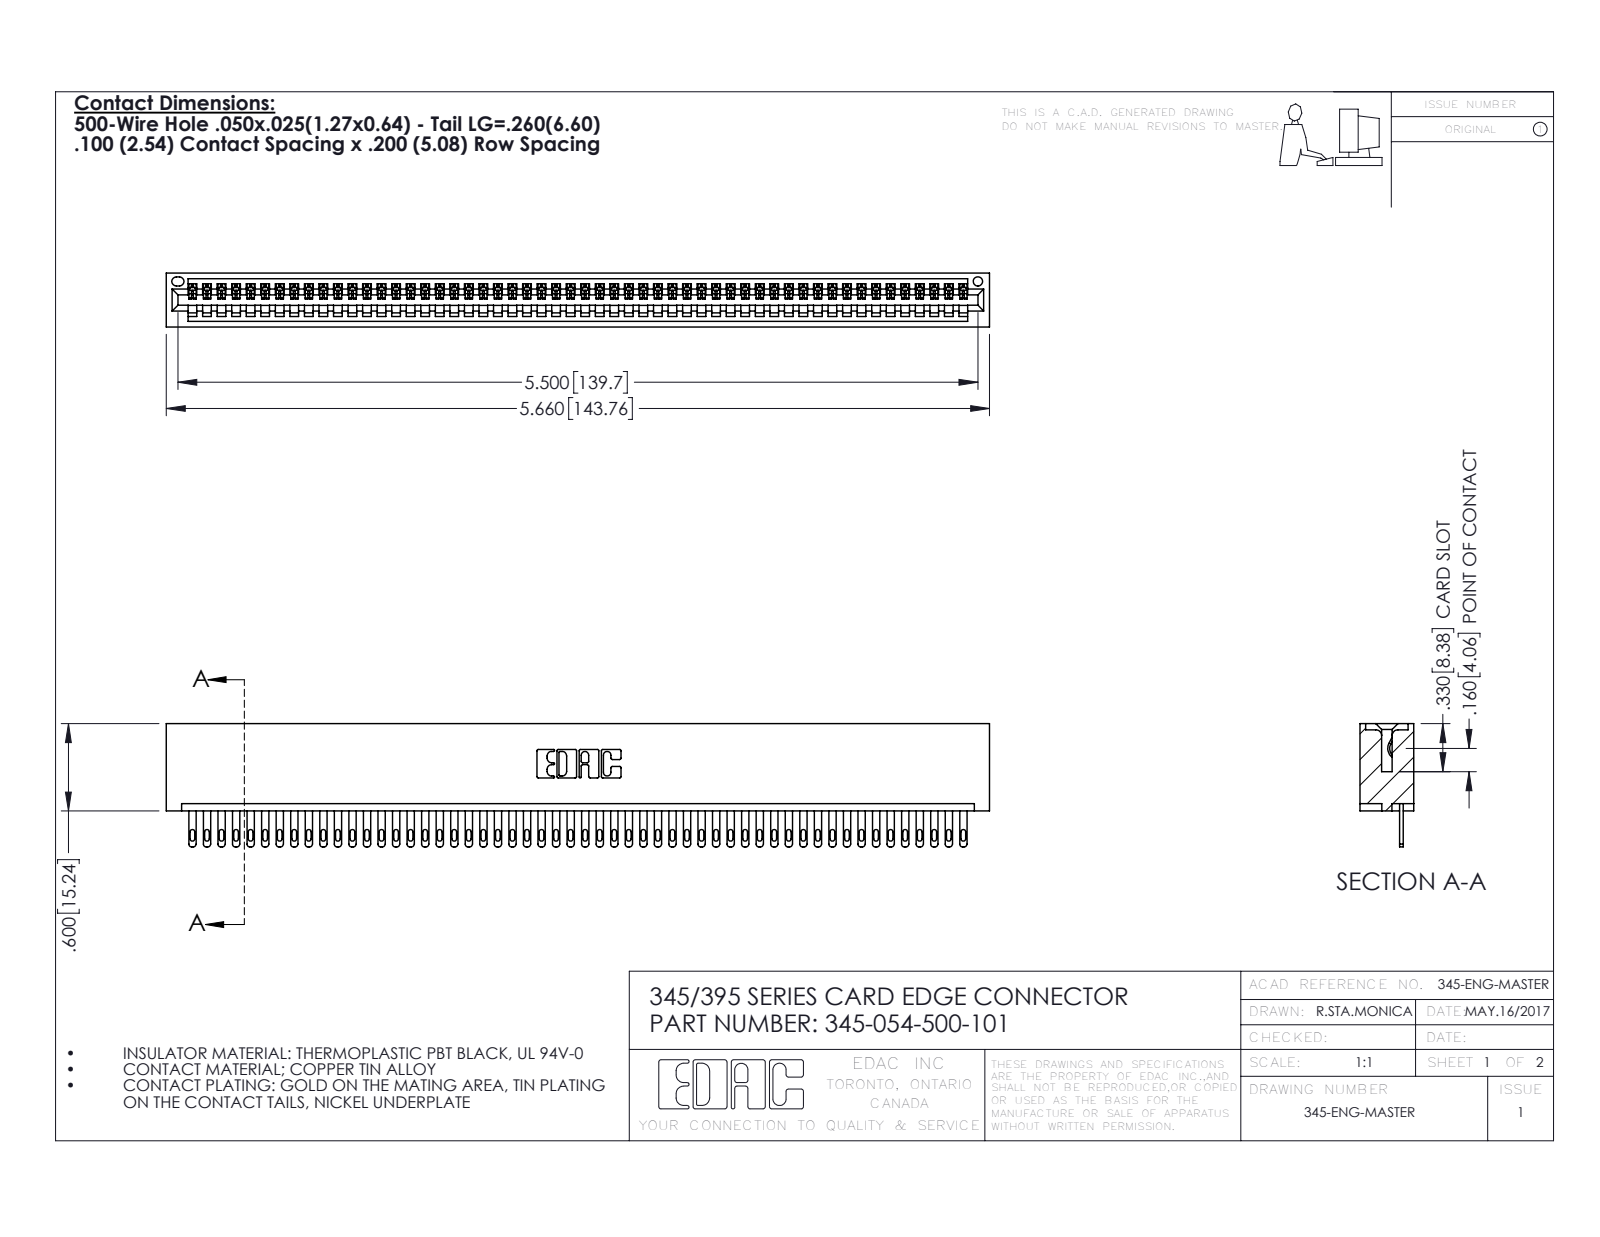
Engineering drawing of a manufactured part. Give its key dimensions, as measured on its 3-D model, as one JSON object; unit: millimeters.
{"part_name": "345-054-500-101; 345 Part_No Mounting Lugs; 345-292-001_345-293-100", "step_written_by": "SolidWorks 2016 (CONFIG_CONTROL_DESIGN)", "units": "millimeters", "bodies": {"solids": 55, "faces": 3034, "planar": 1912, "cylindrical": 1122, "other": 0}, "overall_size": [143.8, 21.5, 9.4], "volume_mm3": 14400, "surface_area_mm2": 19570, "round_holes": [[1.6, 1]], "partial_cylinders_radius": [[0.2, 108], [0.4, 108], [0.5, 108], [0.3, 22], [0.2, 6], [0.8, 6], [0.7, 3], [0.8, 2]], "face_to_face_distances": [1.8, 7.6, 9.4, 2.5, 6.9, 0.6, 5.1, 5.7, 3.8, 1.8]}
